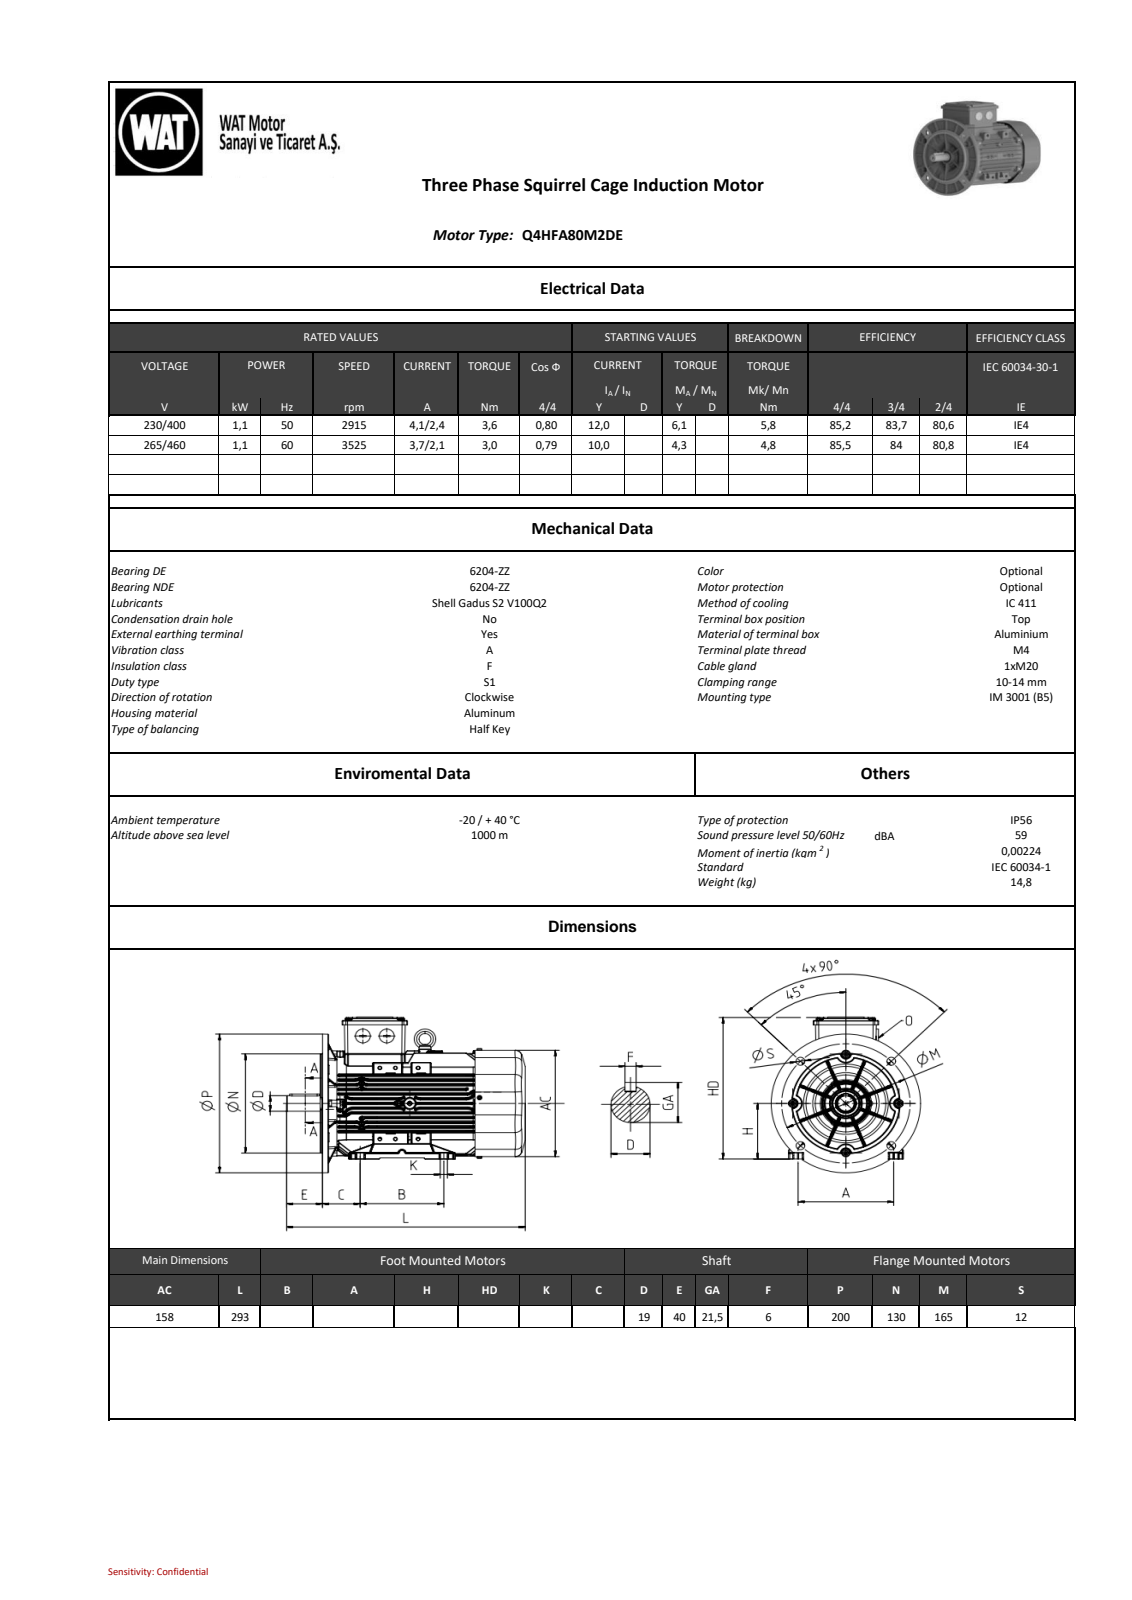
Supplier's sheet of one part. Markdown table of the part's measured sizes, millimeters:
| quantity | value |
| --- | --- |
| part name | model1 |
| STEP written by | SIEMENS PLM Software NX2206.8101 (AUTOMOTIVE_DESIGN) |
| units | millimeters |
| bodies | 0 solids, 6011 faces (1122 planar, 1612 cylindrical, 3277 other) |
| overall size | 293 × 235.5 × 200 |
| round holes (diameter × count) | 3 × 3, 3.5 × 2, 4.6 × 2, 5 × 2, 8 × 1, 57 × 1 |
| round bosses / shafts (diameter × count) | 6 × 5, 21.38 × 2, 8.33 × 2, 146.5 × 1, 130 × 1, 61 × 1, 30 × 1, 24.07 × 1 |
| partial cylindrical surfaces (radius × count) | 0.5 × 473, 0.8 × 286, 1 × 224, 2 × 21, 1.5 × 17, 5 × 12, 1.25 × 8, 75.75 × 8 |
| main face-to-face distances | 1, 41.96, 4.1, 157, 156.98, 10.36, 8.05, 3.95, 86, 10.49 |
| hole center spacings | 25.5, 44.17, 44.16, 50.3, 54.45, 70.94 |
